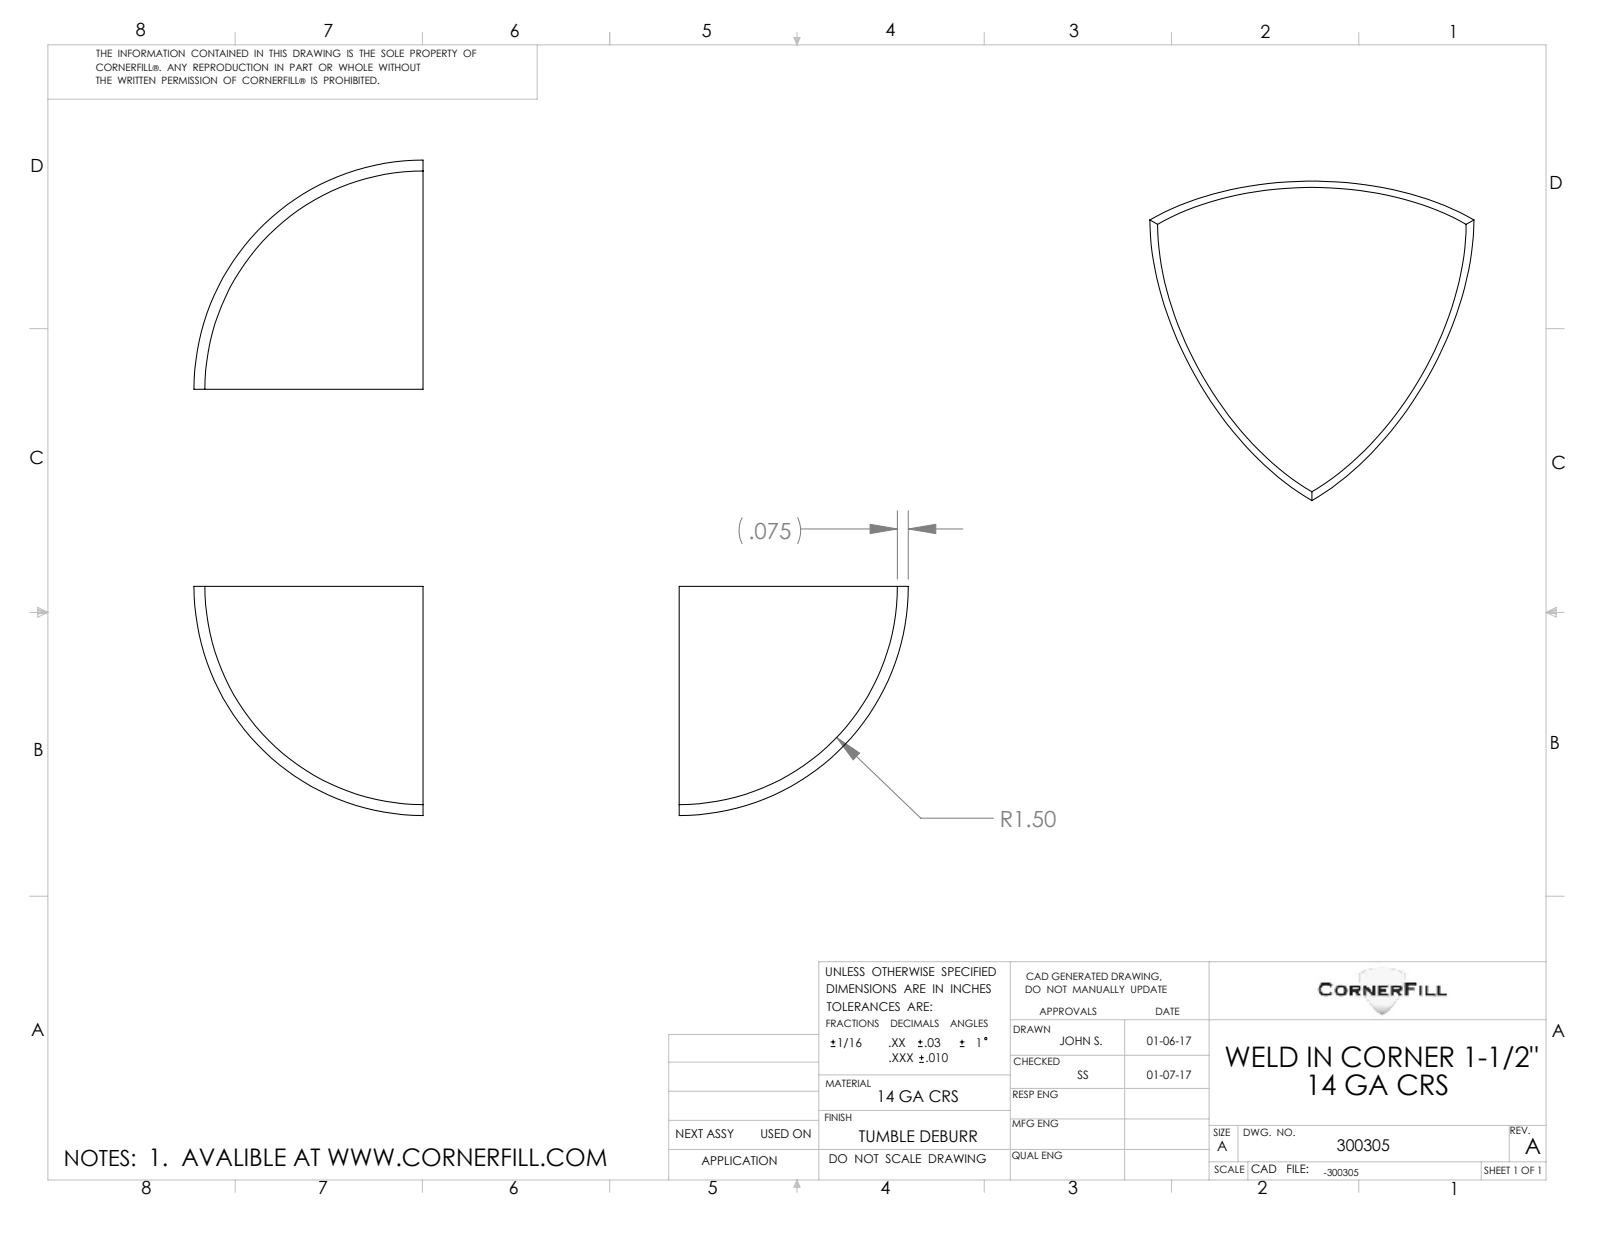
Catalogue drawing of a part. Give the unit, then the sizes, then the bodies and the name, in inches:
Units: inches
Overall size (bounding box): 1.575 × 1.575 × 1.575
Volume: 0.279 in³ · Surface area: 7.974 in²
Bodies: 1 solid, 5 faces (3 planar, 0 cylindrical, 2 other)
Part name (STEP PRODUCT): 300305
STEP written by: SolidWorks 2016 (CONFIG_CONTROL_DESIGN)
